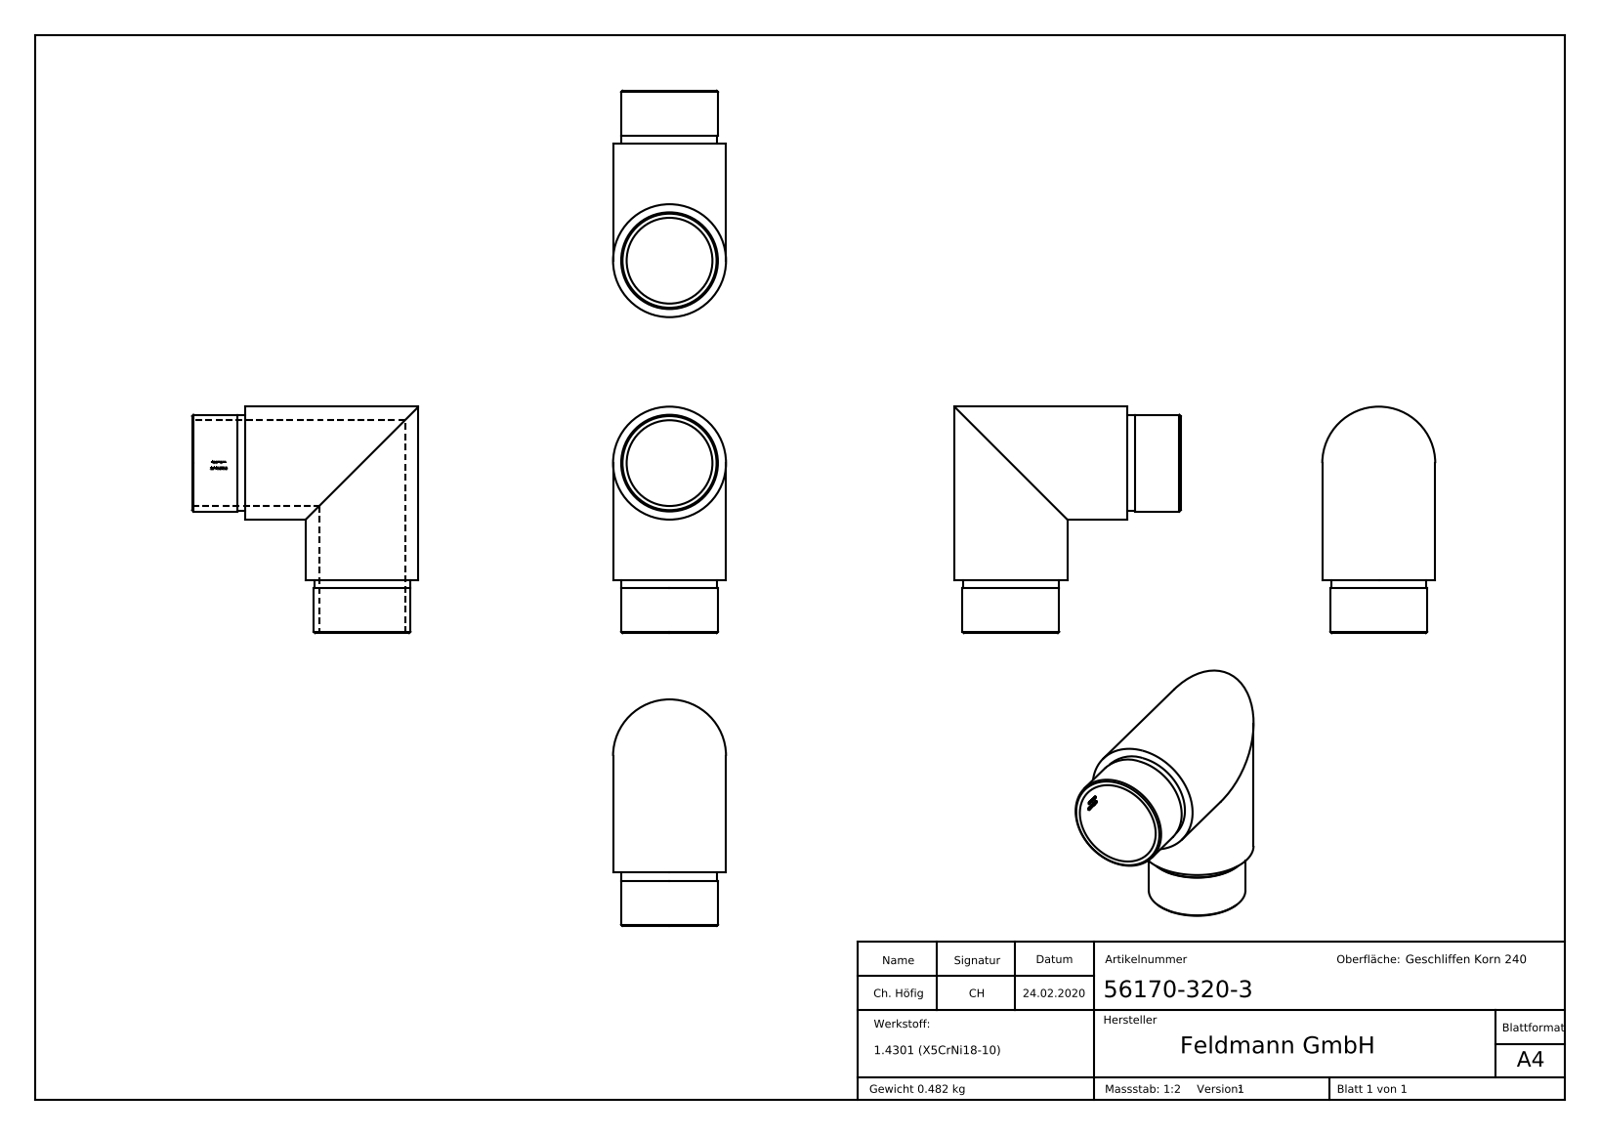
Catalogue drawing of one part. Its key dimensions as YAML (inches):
part_name: "56170-320-3"
step_written_by: "SolidWorks 2015 (CONFIG_CONTROL_DESIGN)"
units: inches
bodies: {solids: 1, faces: 253, planar: 101, cylindrical: 33, other: 119}
overall_size: [3.346, 3.346, 1.669]
volume: 3.723
surface_area: 47.05
round_holes:
  - {diameter: 1.268, count: 2}
round_bosses_or_shafts:
  - {diameter: 1.669, count: 2}
  - {diameter: 1.429, count: 2}
  - {diameter: 1.413, count: 2}
partial_cylinders:
  - {radius: 0.638, count: 1}
face_to_face_distances: [0.787, 0.669, 0.118, 0.07, 0.04, 0.033, 0.037, 0.031, 0.109, 0.119]
